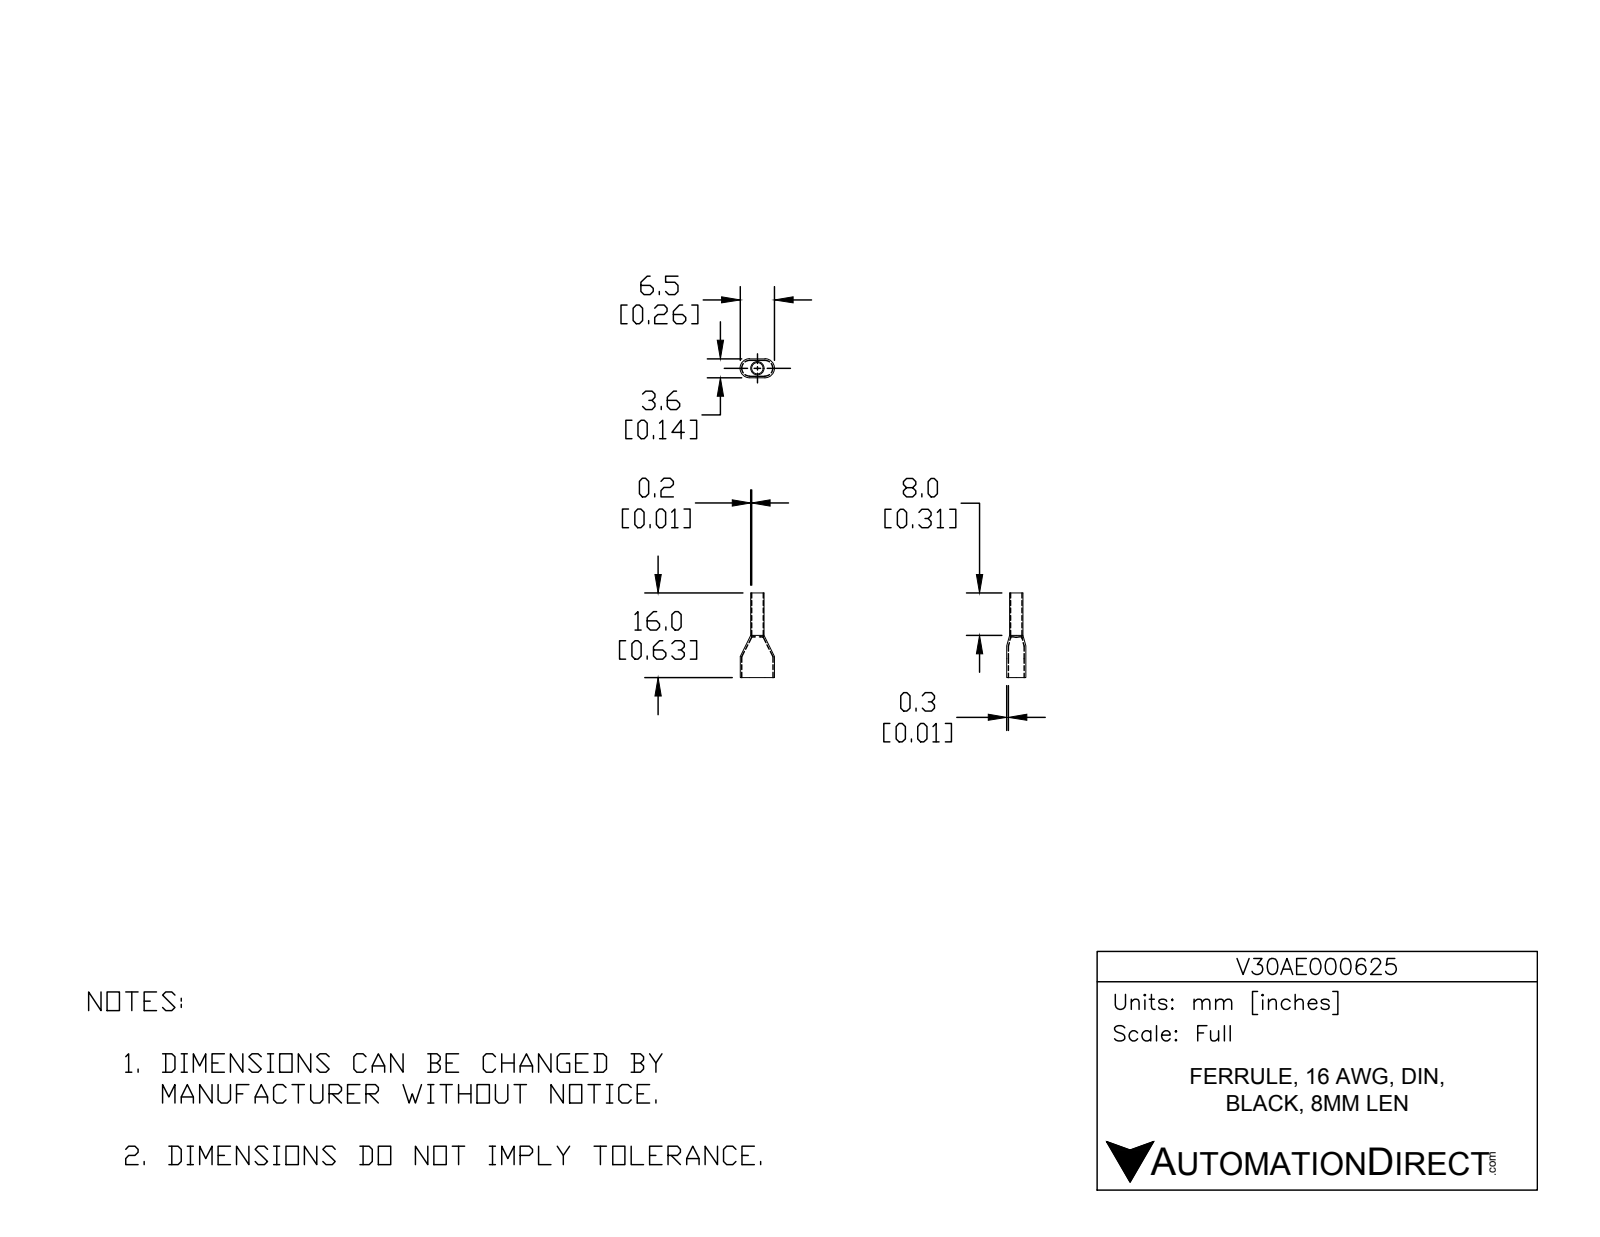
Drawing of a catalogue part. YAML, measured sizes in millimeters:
part_name: "V30AE000625"
step_written_by: "SolidWorks 2017 (AUTOMOTIVE_DESIGN)"
units: millimeters
bodies: {solids: 2, faces: 38, planar: 16, cylindrical: 22, other: 0}
overall_size: [16, 6.5, 3.6]
volume: 43
surface_area: 356
round_holes:
  - {diameter: 2.2, count: 1}
round_bosses_or_shafts:
  - {diameter: 2.5, count: 1}
partial_cylinders:
  - {radius: 1.5, count: 4}
  - {radius: 1.8, count: 4}
face_to_face_distances: [3.3, 3.6, 3, 8, 16, 7.7, 8.3]
